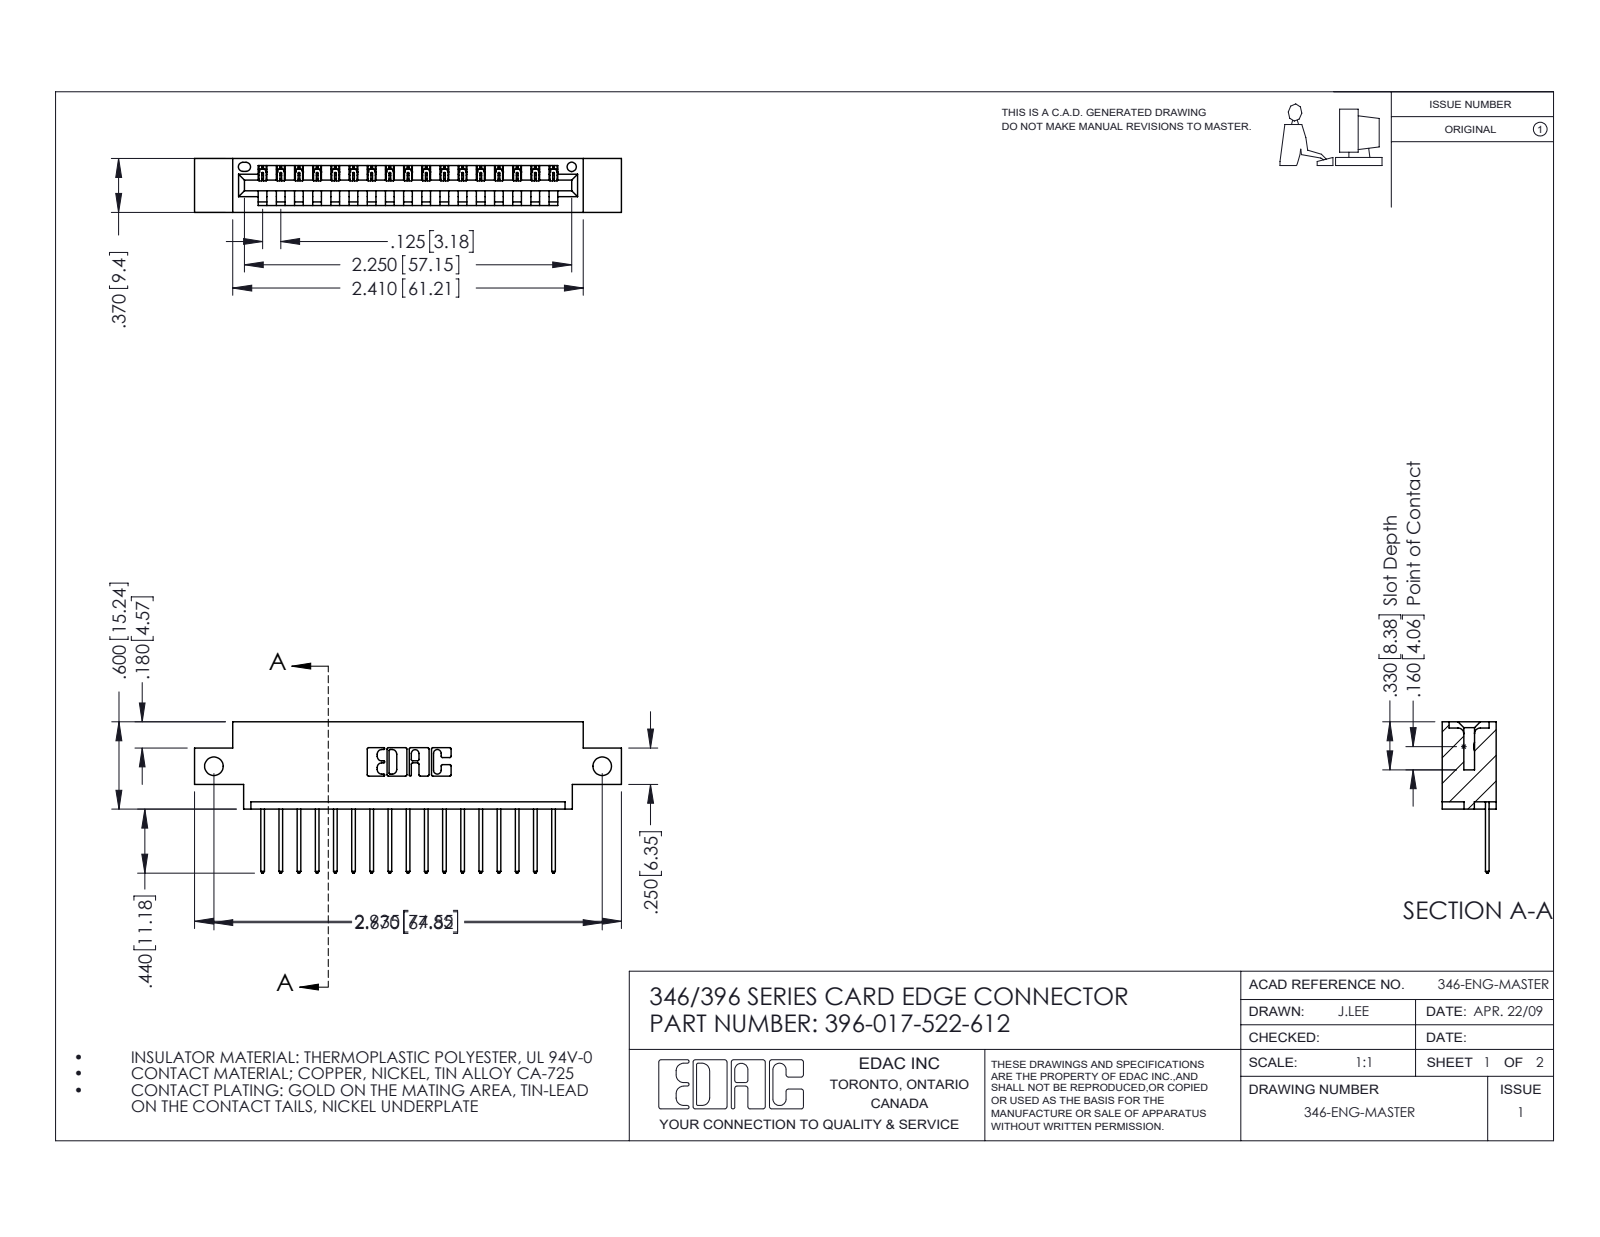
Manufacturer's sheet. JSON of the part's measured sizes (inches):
{"part_name": "346 Part_0.170 Offset - Side Mount; 345-292-001_345-293-122; 396-017-522-612", "step_written_by": "SolidWorks 2016 (CONFIG_CONTROL_DESIGN)", "units": "inches", "bodies": {"solids": 18, "faces": 1112, "planar": 760, "cylindrical": 352, "other": 0}, "overall_size": [2.935, 1.04, 0.37], "volume_in3": 0.41, "surface_area_in2": 12.73, "round_holes": [[0.128, 2], [0.064, 1]], "partial_cylinders_radius": [[0.006, 34], [0.01, 34], [0.01, 22], [0.007, 6], [0.031, 6], [0.026, 3], [0.031, 2], [0.04, 2]], "face_to_face_distances": [0.048, 0.322, 0.37, 0.25, 0.072, 0.298, 0.025, 0.148, 0.222, 0.1], "hole_center_spacings": [2.67]}
